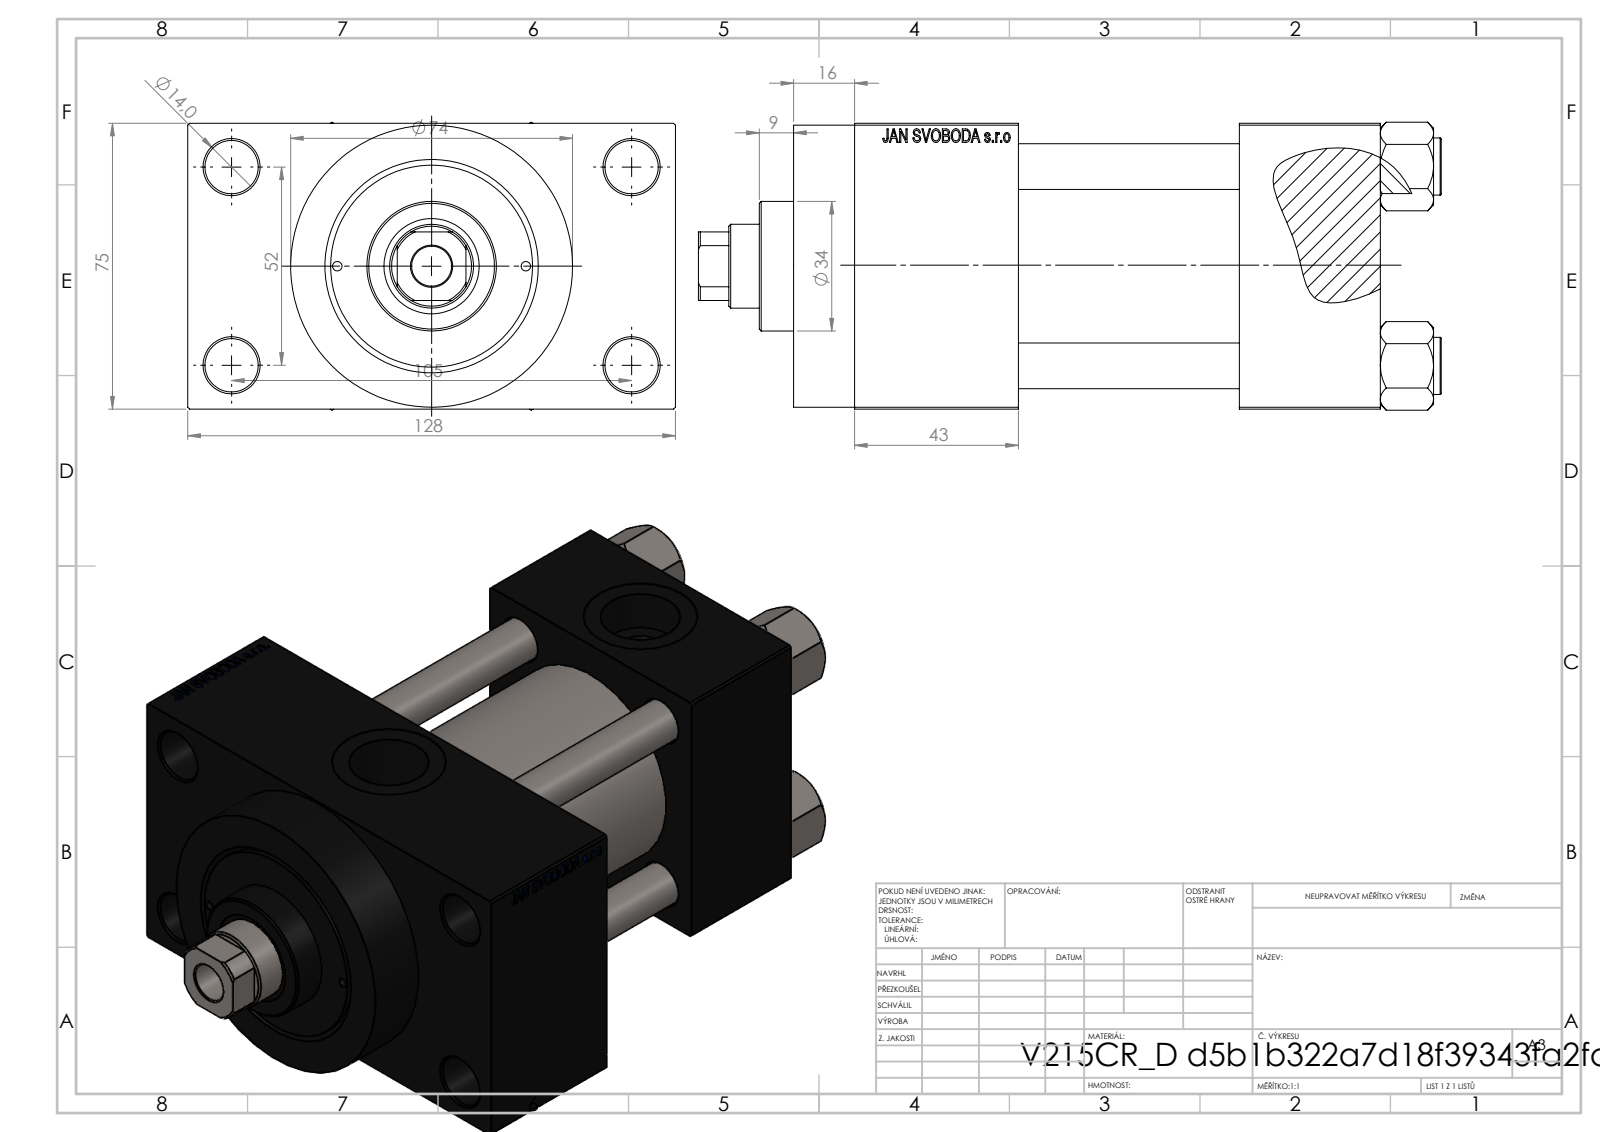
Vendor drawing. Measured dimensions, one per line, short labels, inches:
name: V215CR_VCP_D; NUT_M5_D; V215CR_D_TYCINKA; V215CR_D_Body (+1 more)
written by: SolidWorks 2019 (CONFIG_CONTROL_DESIGN)
unit: in
bodies: 11 solids, 1112 faces (499 planar, 93 cylindrical, 520 other)
size: 7.677 × 5.039 × 2.974
volume: 49.2 in³; area: 255.6 in²
holes: 4× ⌀0.472, 4× ⌀0.551, 2× ⌀0.098, 2× ⌀0.276, 2× ⌀0.825, 2× ⌀1.181, 1× ⌀0.413, 1× ⌀0.866, 1× ⌀0.984, 1× ⌀1.614, 1× ⌀1.969, 1× ⌀2.087
bosses: 4× ⌀0.591, 1× ⌀2.913, 1× ⌀2.205, 1× ⌀1.339
rounds: 1× R0.413
face distances: 2.953, 2.283, 1.457, 3.74, 1.043, 3.996, 5.433, 3.976, 1.693, 0.63
hole spacings: 1.031, 1.037, 1.456, 1.497, 2.059, 2.253, 2.3, 2.307
